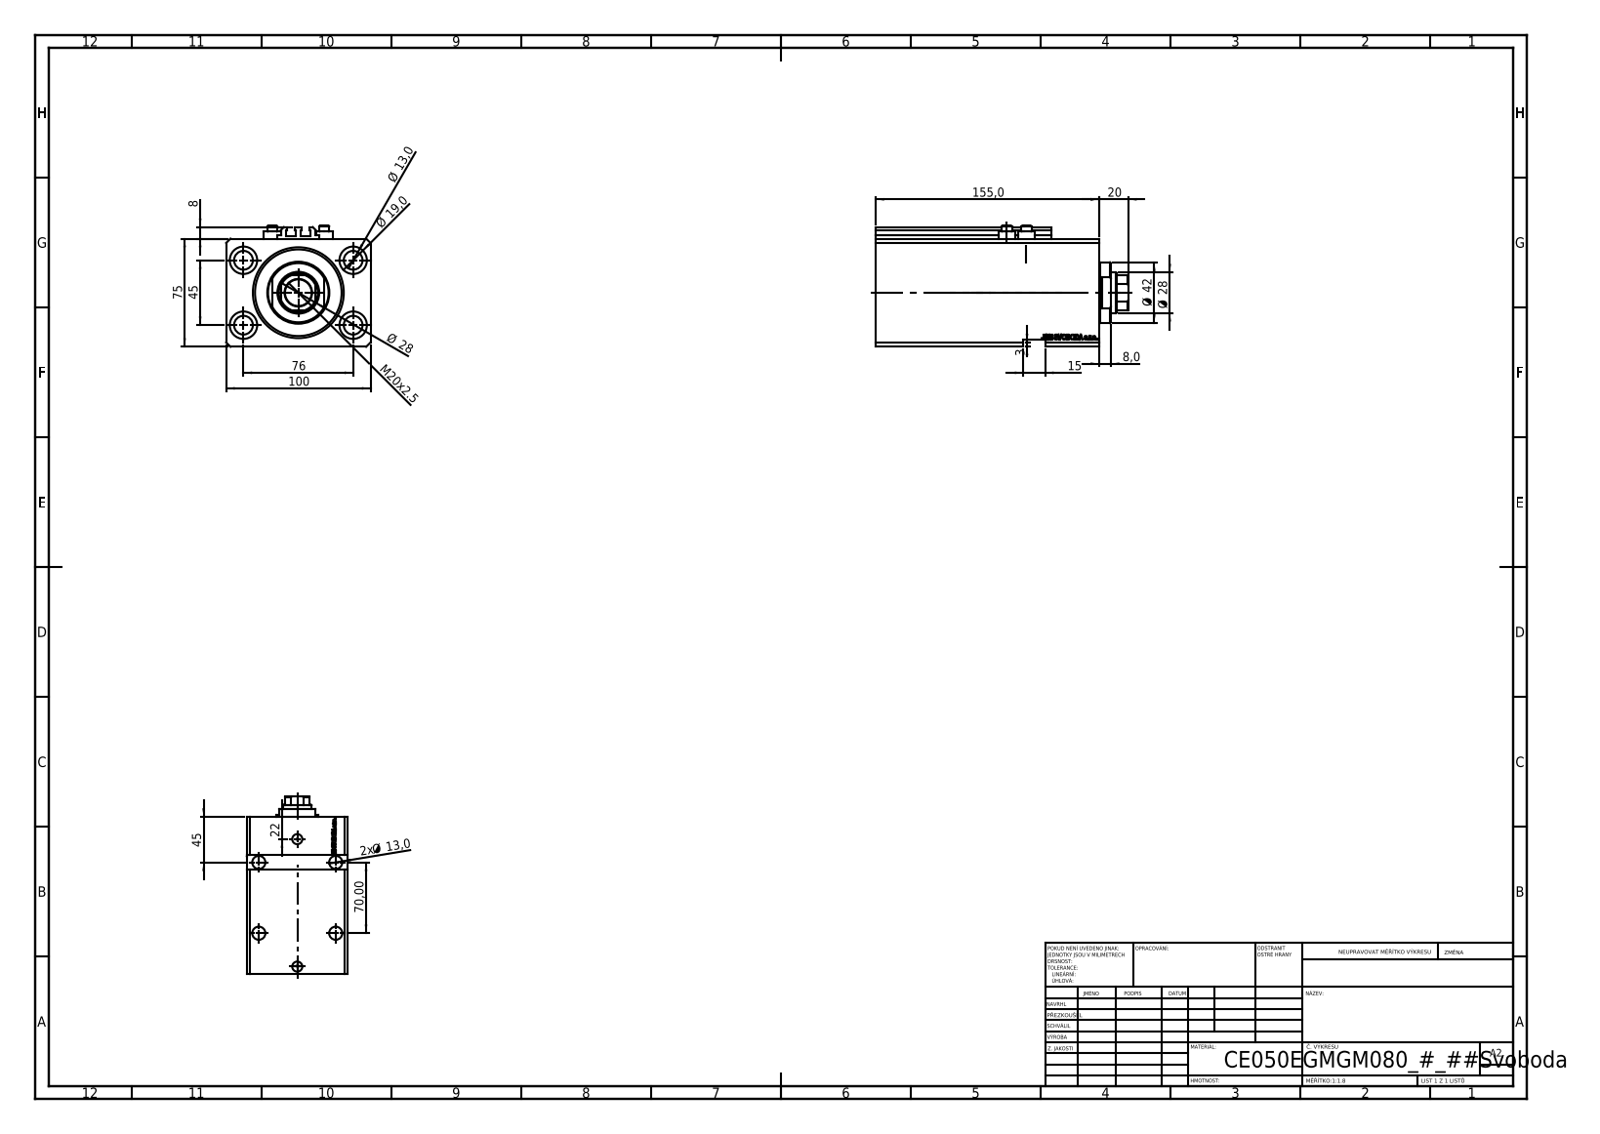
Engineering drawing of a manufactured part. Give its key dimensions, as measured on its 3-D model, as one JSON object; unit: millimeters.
{"part_name": "V250CE_C_VCP; ALLEN BOLT V250CE; V250CE_E_Body; V250CE_VC_E", "step_written_by": "SolidWorks 2019 (CONFIG_CONTROL_DESIGN)", "units": "millimeters", "bodies": {"solids": 8, "faces": 1108, "planar": 535, "cylindrical": 146, "other": 427}, "overall_size": [175, 100, 84], "volume_mm3": 940698, "surface_area_mm2": 175915, "round_holes": [[13, 8], [1.25, 4], [4, 4], [19, 4], [10, 2], [13.16, 2], [20, 2], [18.5, 1], [28, 1], [50, 1], [63, 1]], "round_bosses_or_shafts": [[11.6, 4], [7, 4], [42, 1]], "partial_cylinders_radius": [[0.2, 10], [13.5, 1]], "face_to_face_distances": [75, 100, 155, 20, 11.9, 143.1, 135, 123.1, 8, 80], "hole_center_spacings": [44.16, 76, 13.6, 20.72, 27.59, 33.62, 36, 38.48]}
